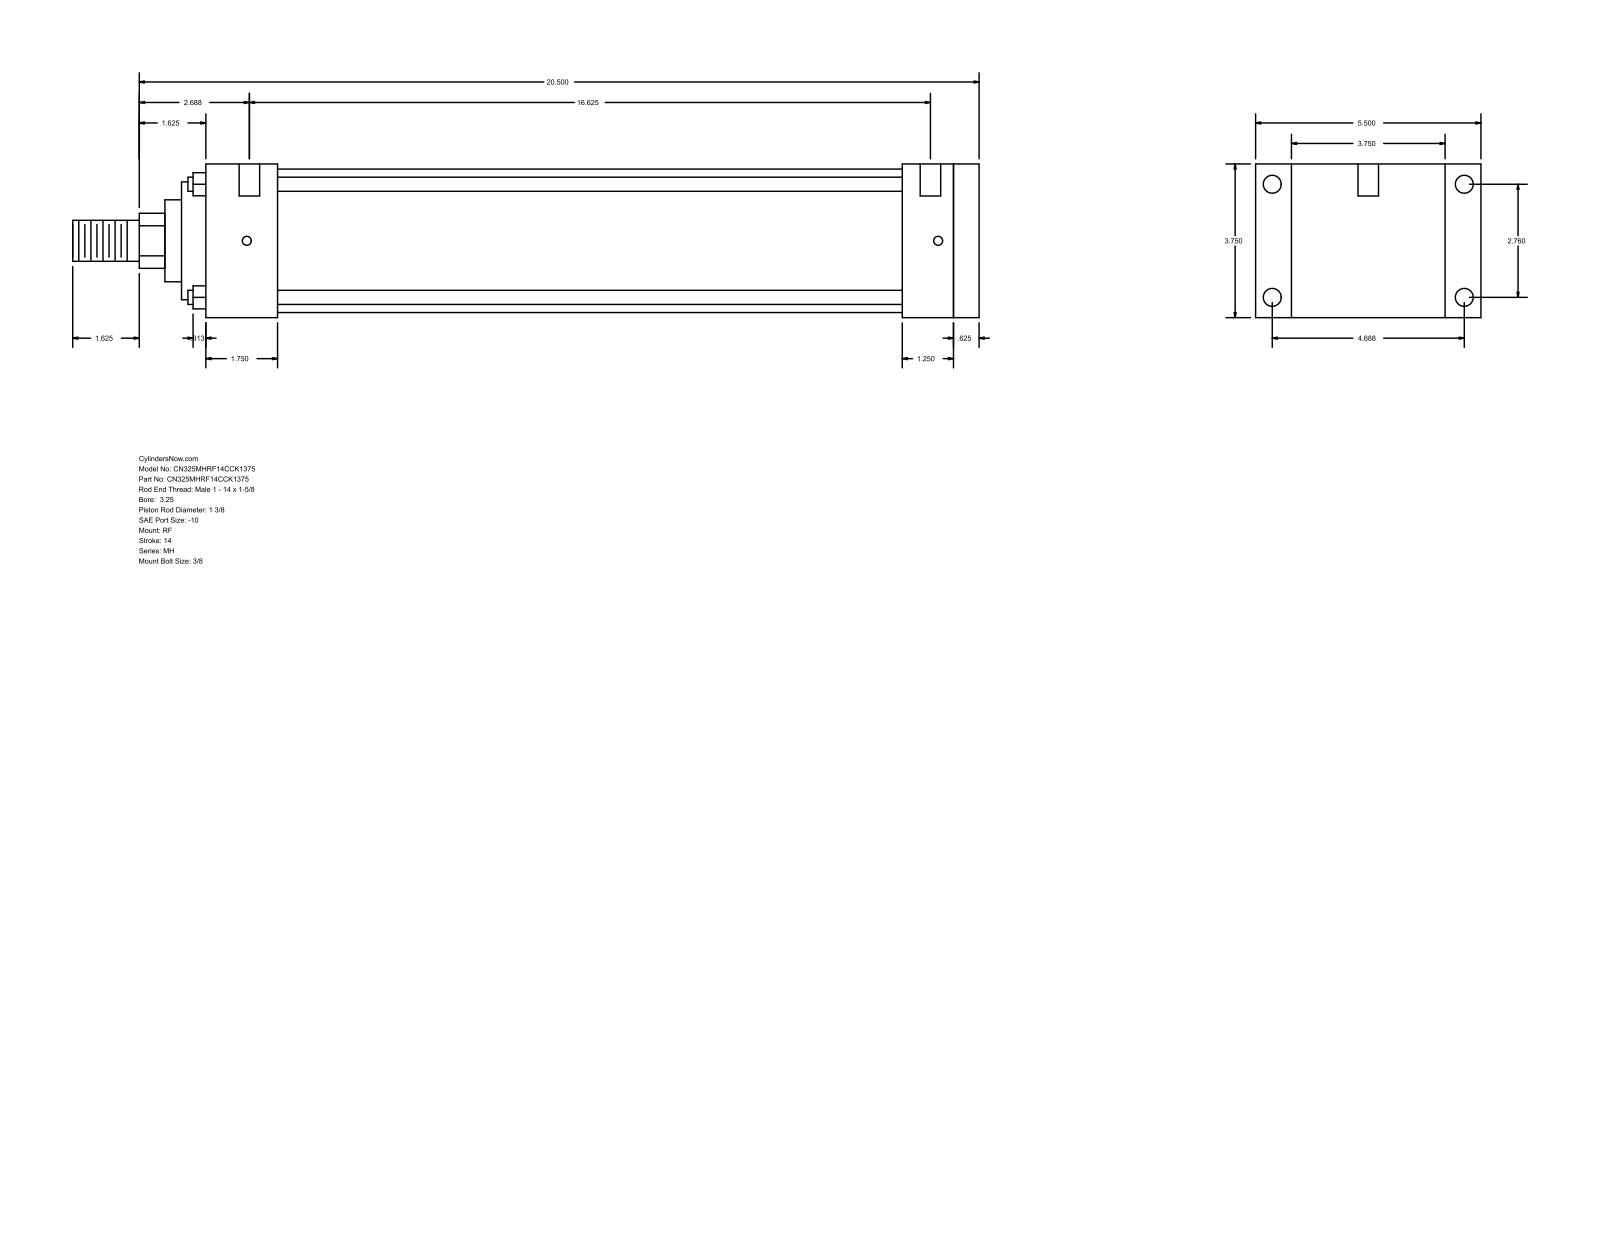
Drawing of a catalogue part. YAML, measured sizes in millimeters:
part_name: "MH_RF__0325_1.375"
step_written_by: "GSSL Pune (CONFIG_CONTROL_DESIGN)"
units: millimeters
bodies: {solids: 0, faces: 94, planar: 65, cylindrical: 29, other: 0}
overall_size: [561.98, 139.7, 95.25]
round_holes:
  - {diameter: 5.56, count: 4}
  - {diameter: 11.13, count: 4}
  - {diameter: 12.7, count: 2}
round_bosses_or_shafts:
  - {diameter: 8.76, count: 4}
  - {diameter: 88.9, count: 1}
  - {diameter: 73.03, count: 1}
  - {diameter: 50.8, count: 1}
  - {diameter: 34.92, count: 1}
  - {diameter: 25.4, count: 1}
partial_cylinders:
  - {radius: 17.06, count: 1}
face_to_face_distances: [95.24, 479.43, 15.88, 463.55, 22.23, 117.47, 44.45, 419.1, 434.98, 431.8]
hole_center_spacings: [70.1, 119.06, 138.16, 428.63, 1.59, 4.76, 422.28, 423.87]
